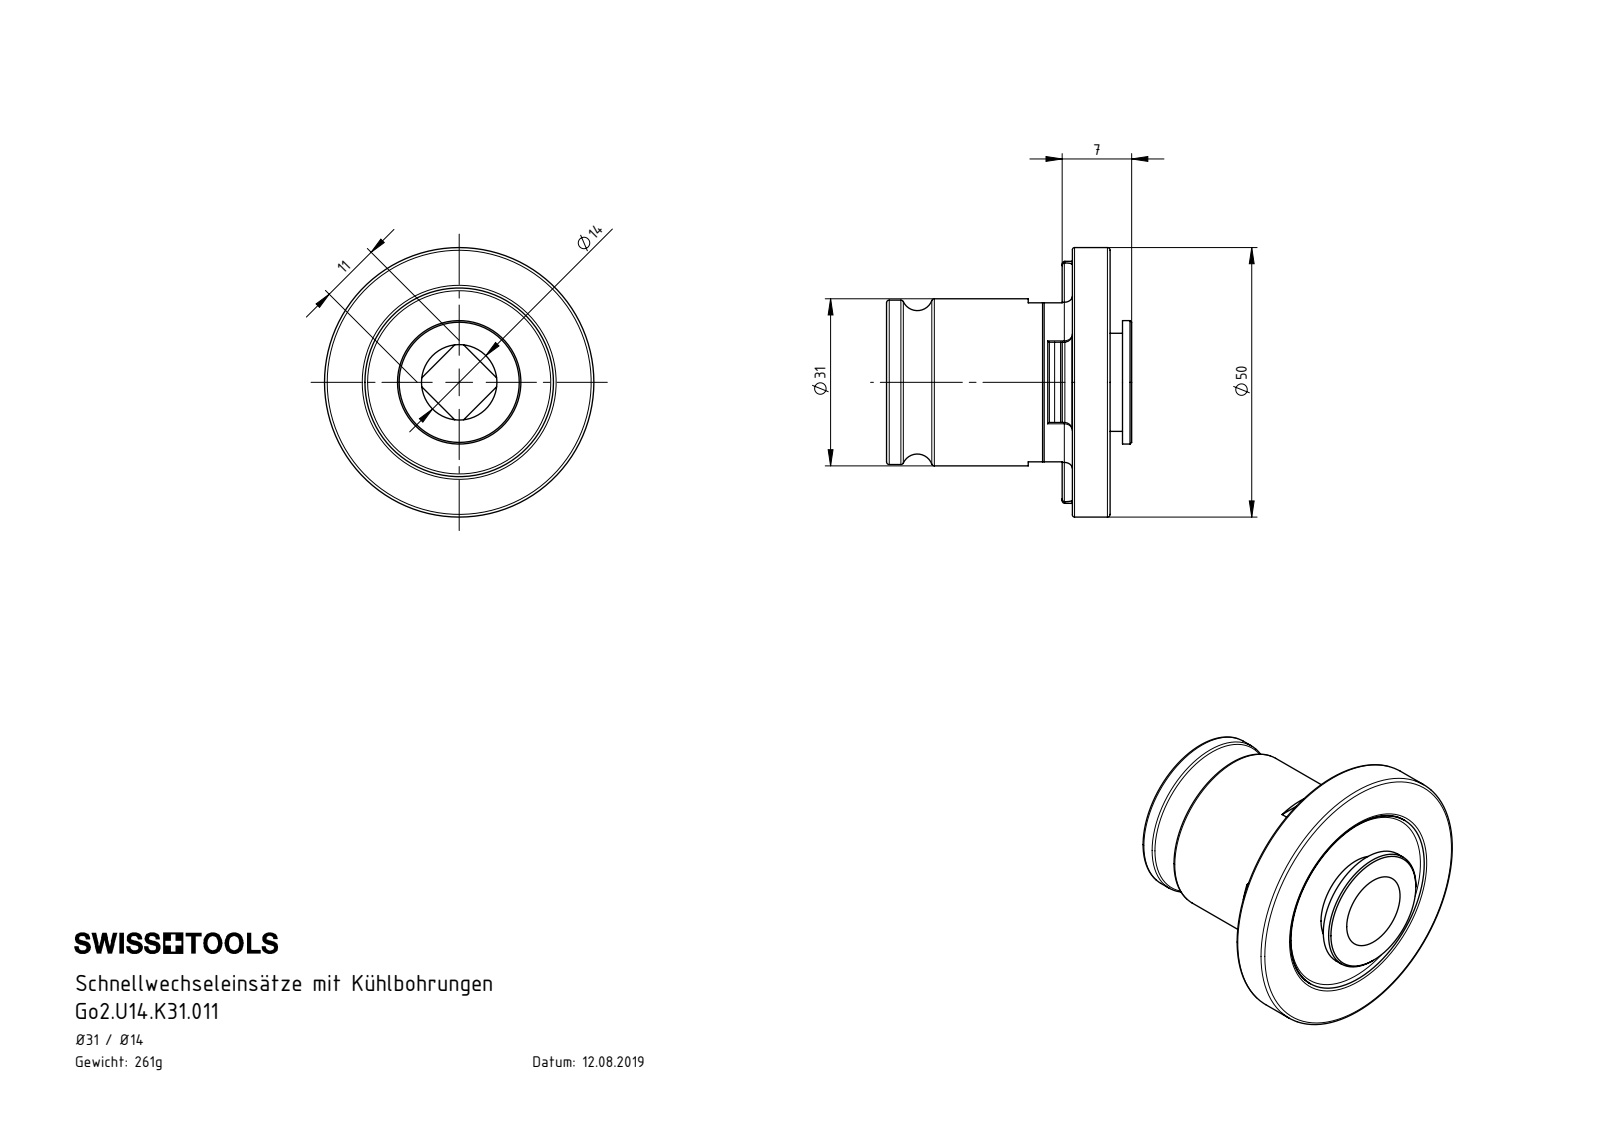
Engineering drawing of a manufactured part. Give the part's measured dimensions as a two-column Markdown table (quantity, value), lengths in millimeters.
| quantity | value |
| --- | --- |
| part name | Go2.U14.K31.011 |
| STEP written by | SolidWorks 2012 (AUTOMOTIVE_DESIGN) |
| units | millimeters |
| bodies | 1 solid, 133 faces (37 planar, 39 cylindrical, 57 other) |
| overall size | 50 × 50 × 45.5 |
| volume | 33 796 mm³ |
| surface area | 10 978 mm² |
| round holes (diameter × count) | 14 × 1, 20.1 × 1 |
| round bosses / shafts (diameter × count) | 50 × 1, 35 × 1, 31 × 1, 30.6 × 1, 30.5 × 1, 26 × 1, 22.2 × 1 |
| partial cylindrical surfaces (radius × count) | 1.5 × 5, 0.5 × 4, 20 × 1, 22.45 × 1 |
| main face-to-face distances | 7, 6.35, 0.65, 11, 4.65, 4, 34.5, 40.85, 41.5, 45.5 |
